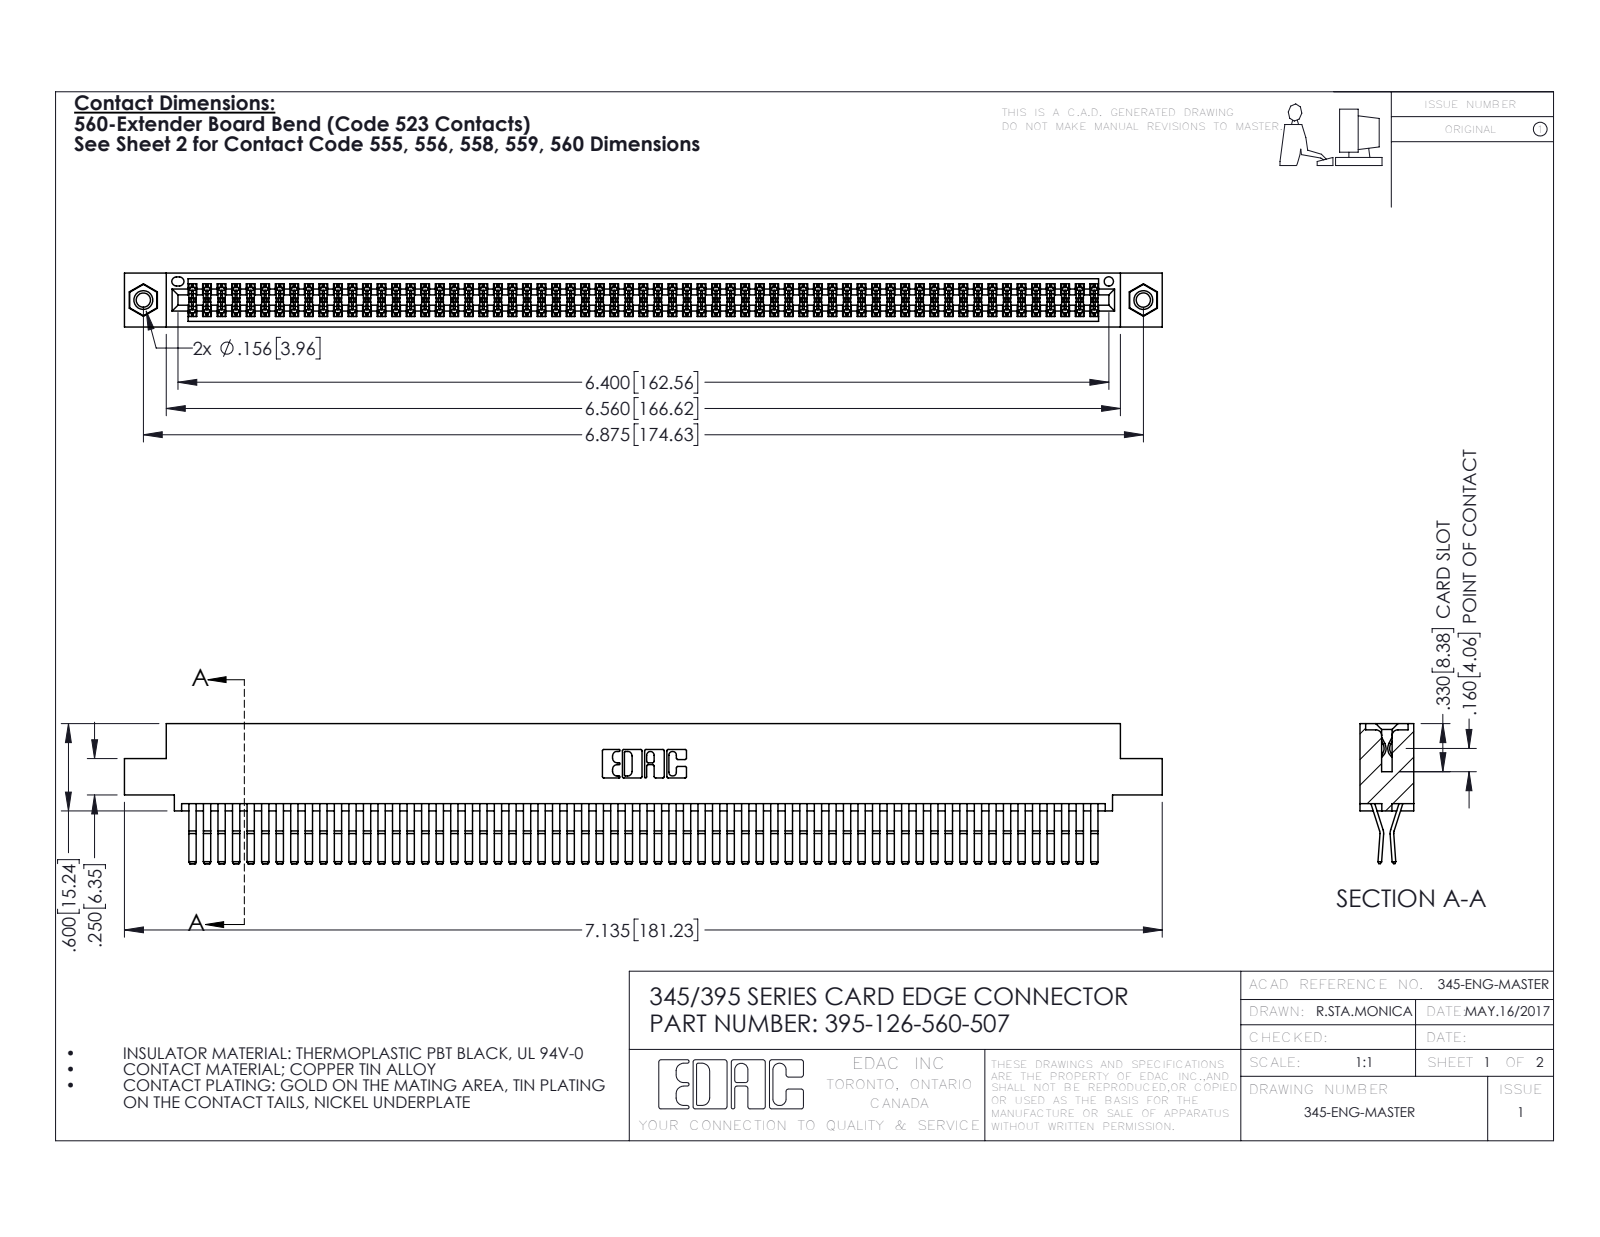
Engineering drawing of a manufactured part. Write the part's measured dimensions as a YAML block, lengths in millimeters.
part_name: "345 Part_0.110 Offset - 0.156 Dia-TI; 345-250-001_345-250-005-103; 395-126-560-507; 345-292-001_560 Tail"
step_written_by: "SolidWorks 2016 (CONFIG_CONTROL_DESIGN)"
units: millimeters
bodies: {solids: 129, faces: 6742, planar: 4274, cylindrical: 2452, other: 16}
overall_size: [181.2, 24.4, 9.4]
volume: 18530
surface_area: 30060
round_holes:
  - {diameter: 2.5, count: 2}
  - {diameter: 3.2, count: 2}
  - {diameter: 4, count: 2}
  - {diameter: 1.6, count: 1}
round_bosses_or_shafts:
  - {diameter: 3.9, count: 2}
partial_cylinders:
  - {radius: 0.2, count: 190}
  - {radius: 0.3, count: 22}
  - {radius: 0.2, count: 6}
  - {radius: 0.8, count: 6}
  - {radius: 0.7, count: 3}
  - {radius: 0.3, count: 2}
  - {radius: 0.4, count: 2}
  - {radius: 0.5, count: 2}
face_to_face_distances: [0.6, 1.8, 7.6, 9.4, 5.1, 2.5, 6.9, 5.7, 4.4, 3.8]
hole_center_spacings: [6.9, 168.6, 174.6]
